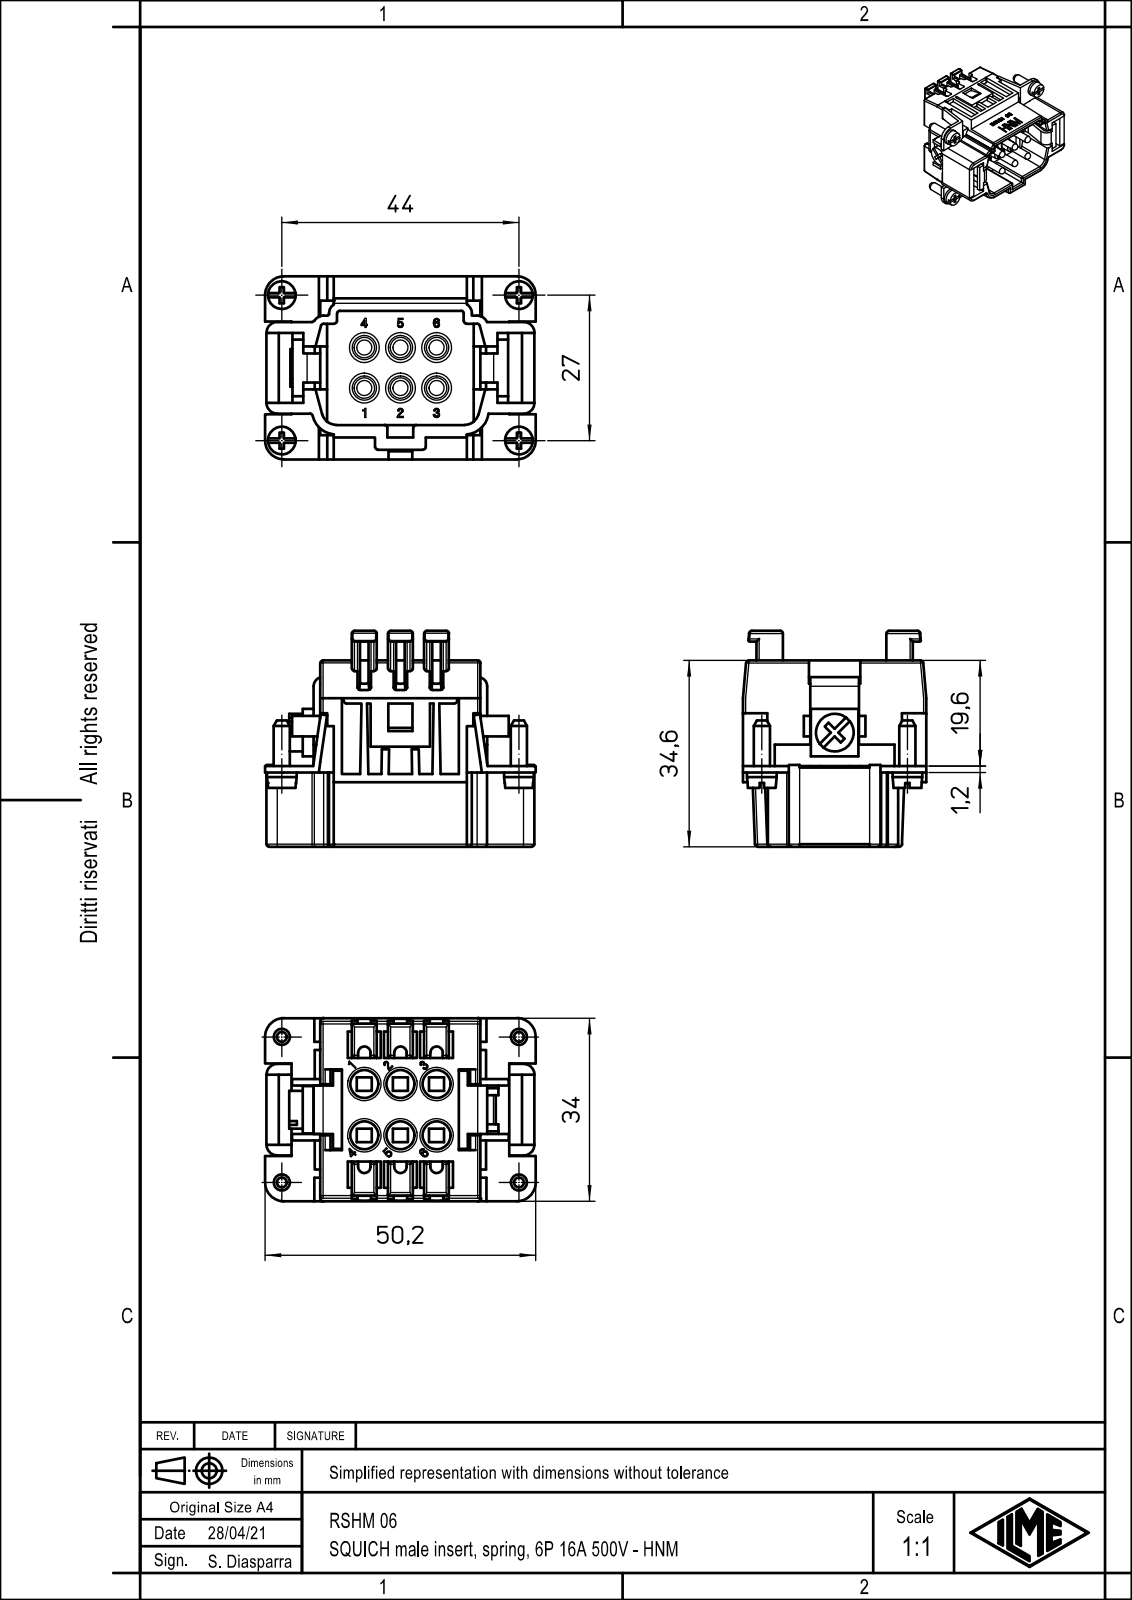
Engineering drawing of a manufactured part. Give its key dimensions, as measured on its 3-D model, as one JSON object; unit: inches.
{"part_name": "RSHM_06", "step_written_by": "Creo Elements/Direct Modeling 20.1B 02-Apr-2019 (C) Parametric Technology GmbH (AUTOMOTIVE_DESIGN)", "units": "inches", "bodies": {"solids": 1, "faces": 1154, "planar": 732, "cylindrical": 269, "other": 153}, "overall_size": [1.976, 1.579, 1.339], "volume_in3": 1.591, "surface_area_in2": 25.23, "round_holes": [[0.205, 6], [0.13, 1]], "round_bosses_or_shafts": [[0.098, 6], [0.217, 4], [0.118, 4], [0.276, 1]], "partial_cylinders_radius": [[0.02, 90], [0.012, 15], [0.008, 14], [0.079, 10], [0.045, 6], [0.138, 4], [0.039, 2], [0.051, 2]], "face_to_face_distances": [0.047, 0.059, 1.087, 0.252, 0.098, 0.492, 0.335, 0.413, 1.169, 0.02], "hole_center_spacings": [0.264, 0.457, 0.374, 0.528, 0.647]}
